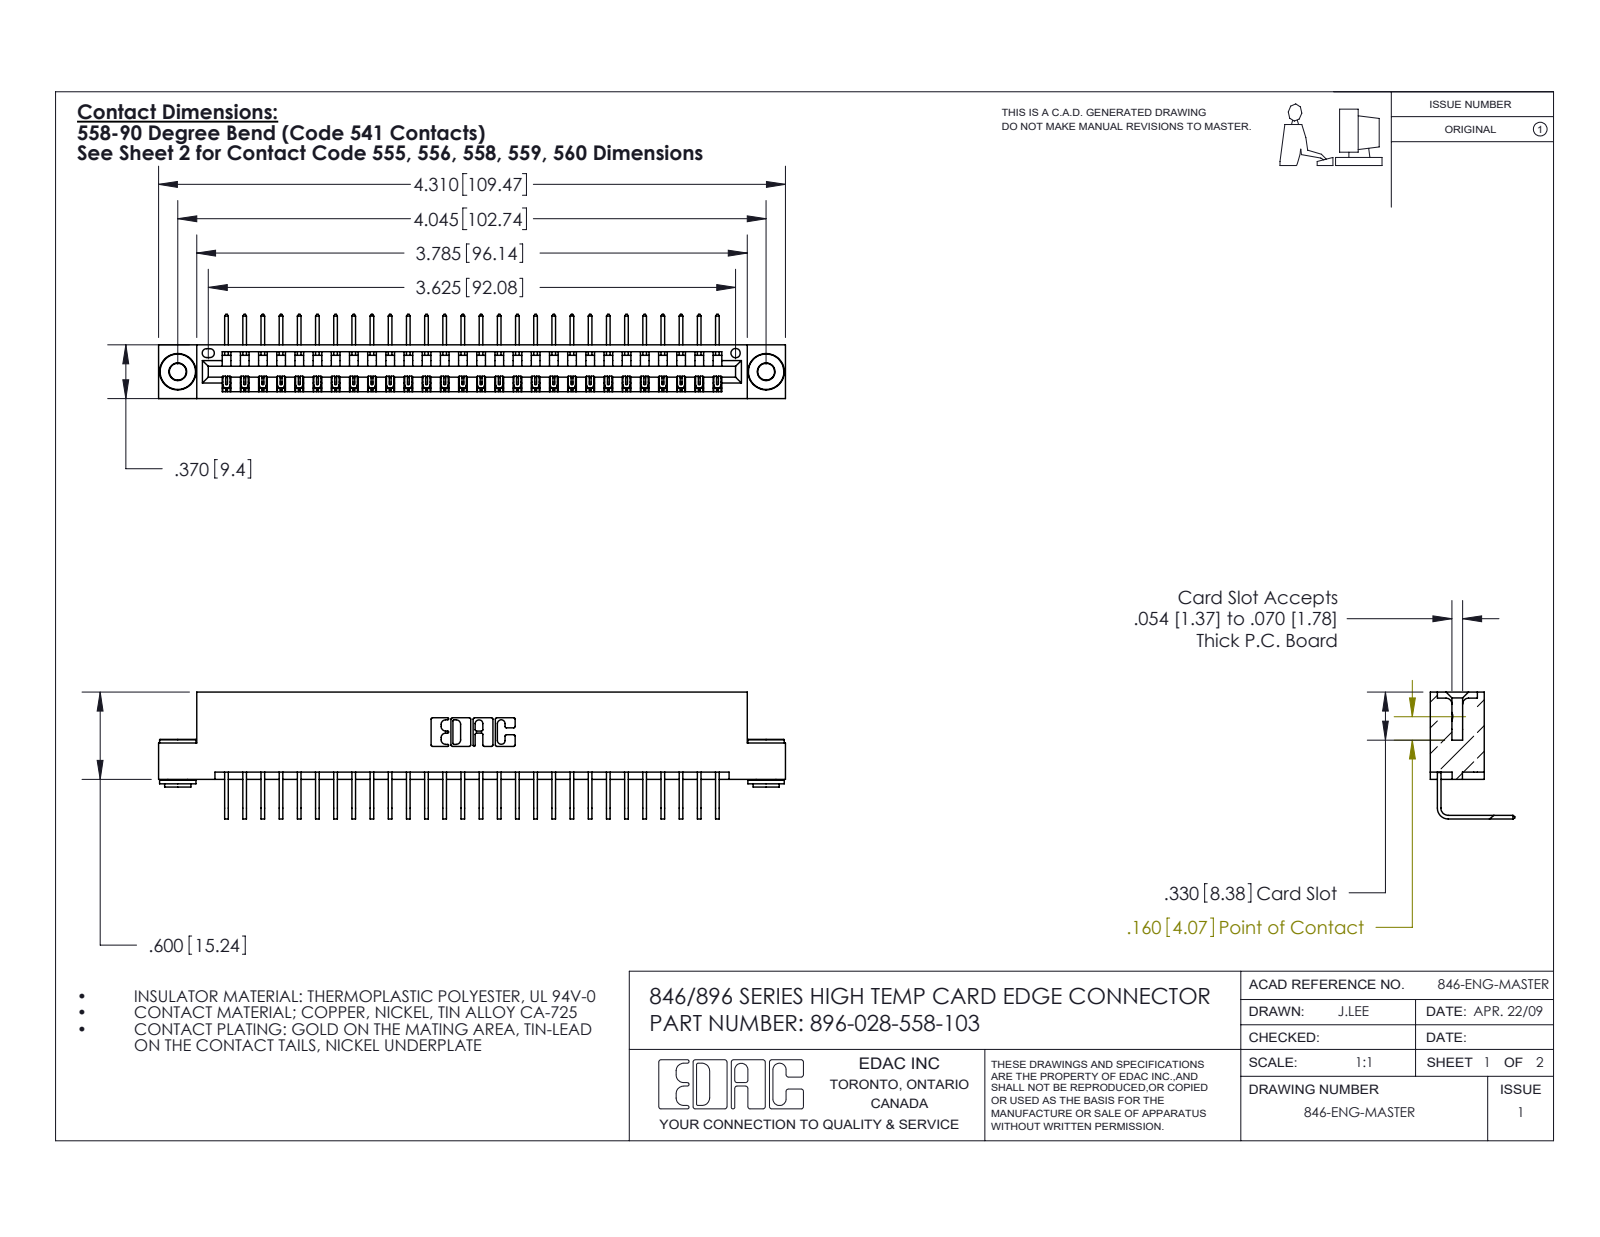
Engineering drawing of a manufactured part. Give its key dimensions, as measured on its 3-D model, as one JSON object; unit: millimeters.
{"part_name": "346 Part_Flush Mounting Lugs - 0.156 Dia-TH; 345-250-002_345-250-002-102; 345-292-001_558 Tail - 2; 396-028-558-103", "step_written_by": "SolidWorks 2016 (CONFIG_CONTROL_DESIGN)", "units": "millimeters", "bodies": {"solids": 31, "faces": 1840, "planar": 1262, "cylindrical": 570, "other": 8}, "overall_size": [109.5, 22.2, 14.7], "volume_mm3": 10500, "surface_area_mm2": 13740, "round_holes": [[2.9, 2], [4, 2], [1.6, 1]], "round_bosses_or_shafts": [[6.4, 2], [4.6, 2], [3.5, 2]], "partial_cylinders_radius": [[0.2, 56], [0.3, 22], [0.2, 6], [0.8, 6], [0.7, 3], [0.8, 2], [1, 2], [0.4, 1]], "face_to_face_distances": [8.2, 1.2, 9.4, 6.4, 0.6, 7.6, 1.8, 3.8, 5.6, 2.5], "hole_center_spacings": [6.2, 97.5, 102.7]}
